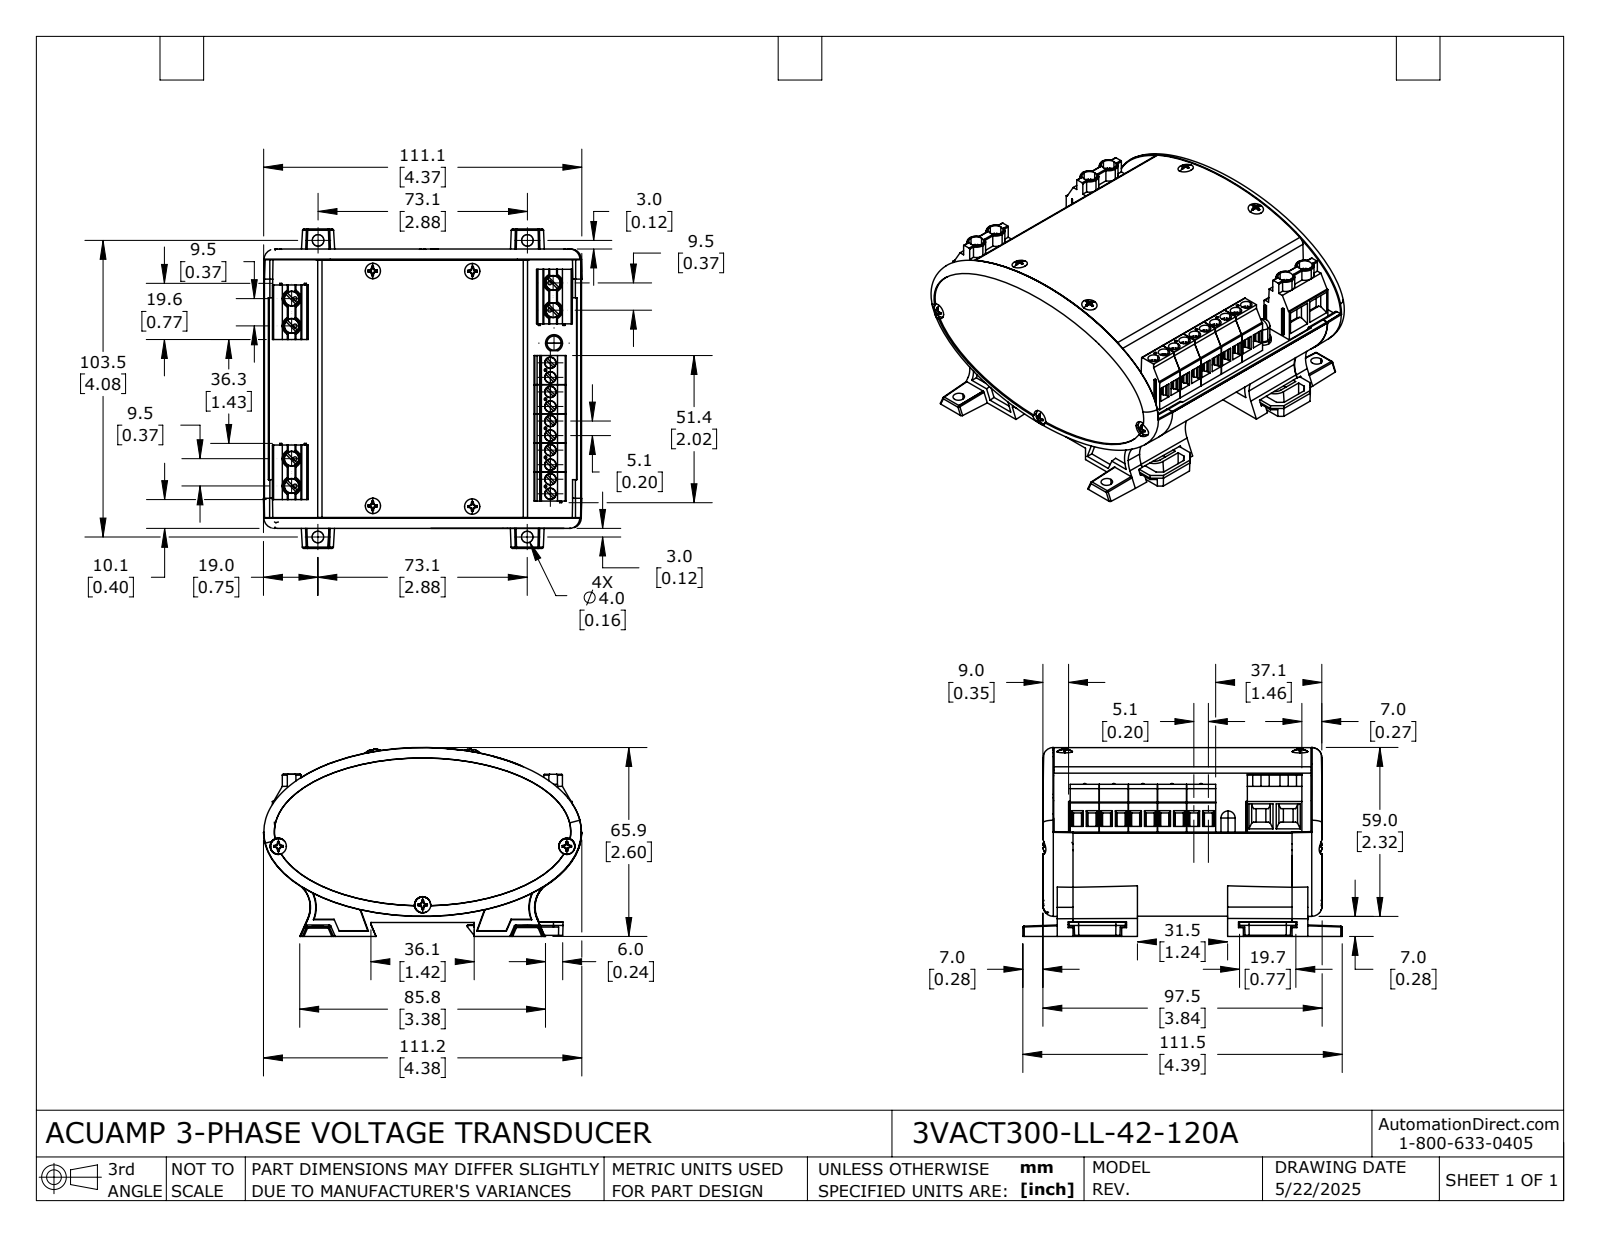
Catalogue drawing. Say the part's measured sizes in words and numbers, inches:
The part is named "3VACT300-LL-42-120A". Its 3-D file was written by "SolidWorks 2024 (AUTOMOTIVE_DESIGN)". It is 26 solids with 2967 faces: 1482 planar, 844 cylindrical and 641 other. Overall it measures 7.429 by 4.374 by 2.597 inches. Its volume is 11.76 cubic inches and its surface area 284.7 square inches. Round holes: 12 of diameter 0.05, 10 of diameter 0.157, 6 of diameter 0.08, 6 of diameter 0.205, 4 of diameter 0.126, 3 of diameter 0.111, 3 of diameter 0.28. Round bosses or shafts: 16 of diameter 0.051, 10 of diameter 0.15, 10 of diameter 0.112, 10 of diameter 0.067, 6 of diameter 0.197, 4 of diameter 0.018, 1 of diameter 0.234, 1 of diameter 0.194. Partial cylindrical surfaces (rounded edges, fillets, slot ends): 38 of radius 0.006, 20 of radius 0.039, 17 of radius 0.02, 12 of radius 0.008, 8 of radius 0.012, 6 of radius 0.01, 6 of radius 0.128, 4 of radius 0.018. The main face-to-face distances are 0.063, 0.128, 6.709, 0.084, 6.838, 6.581, 0.394, 6.444, 0.266, 6.315. The hole center spacings are 0.2, 0.4, 0.6, 0.8, 1, 1.2, 0.2, 0.2.
